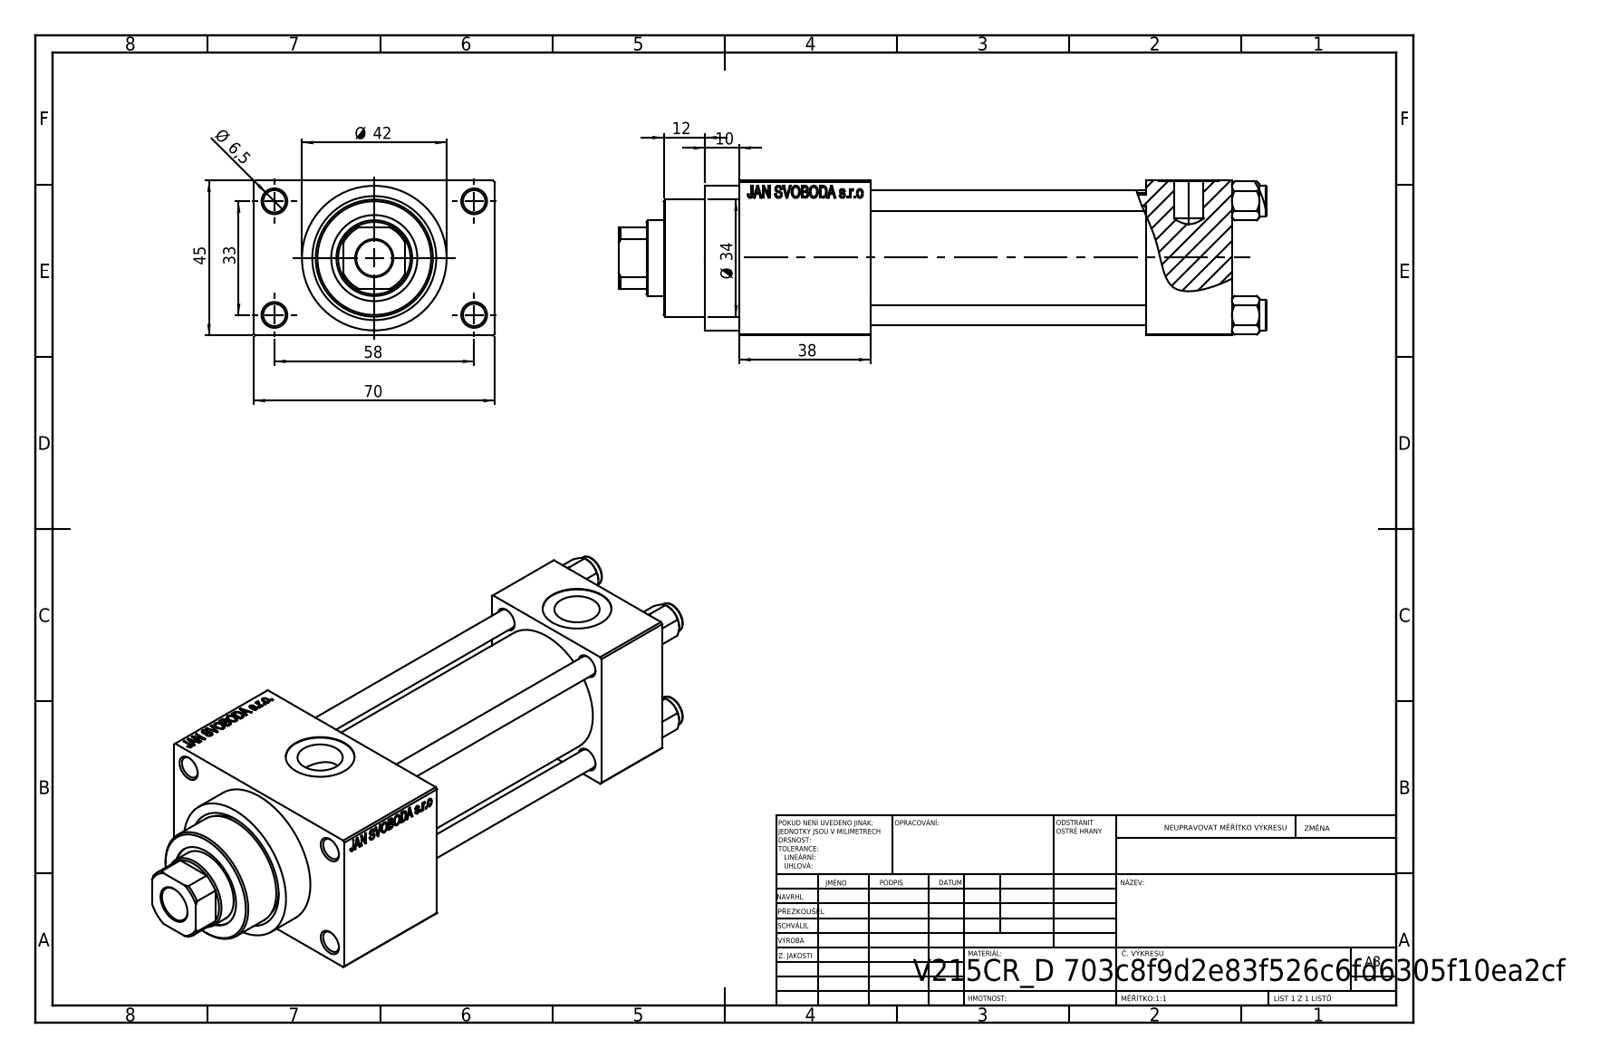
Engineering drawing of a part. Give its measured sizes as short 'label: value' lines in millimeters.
name: NUT_M5_D; V215CR_D_TYCINKA; V215CR_D_Body; V215_VC_A (+1 more)
written by: SolidWorks 2019 (CONFIG_CONTROL_DESIGN)
unit: mm
bodies: 11 solids, 1105 faces (496 planar, 89 cylindrical, 520 other)
size: 188 × 70 × 45
volume: 269 189 mm³; area: 90 301 mm²
holes: 4× ⌀6, 4× ⌀6.5, 2× ⌀7, 2× ⌀13.16, 2× ⌀20, 1× ⌀10.5, 1× ⌀22, 1× ⌀24, 1× ⌀25, 1× ⌀32, 1× ⌀33
bosses: 4× ⌀9, 1× ⌀42, 1× ⌀38, 1× ⌀34
rounds: 1× R10.5
face distances: 45, 25, 12.5, 57.5, 80, 105, 118, 70, 38, 143
hole spacings: 12.4, 23.48, 33.2, 33.37, 35.35, 45.6, 56.35, 33
